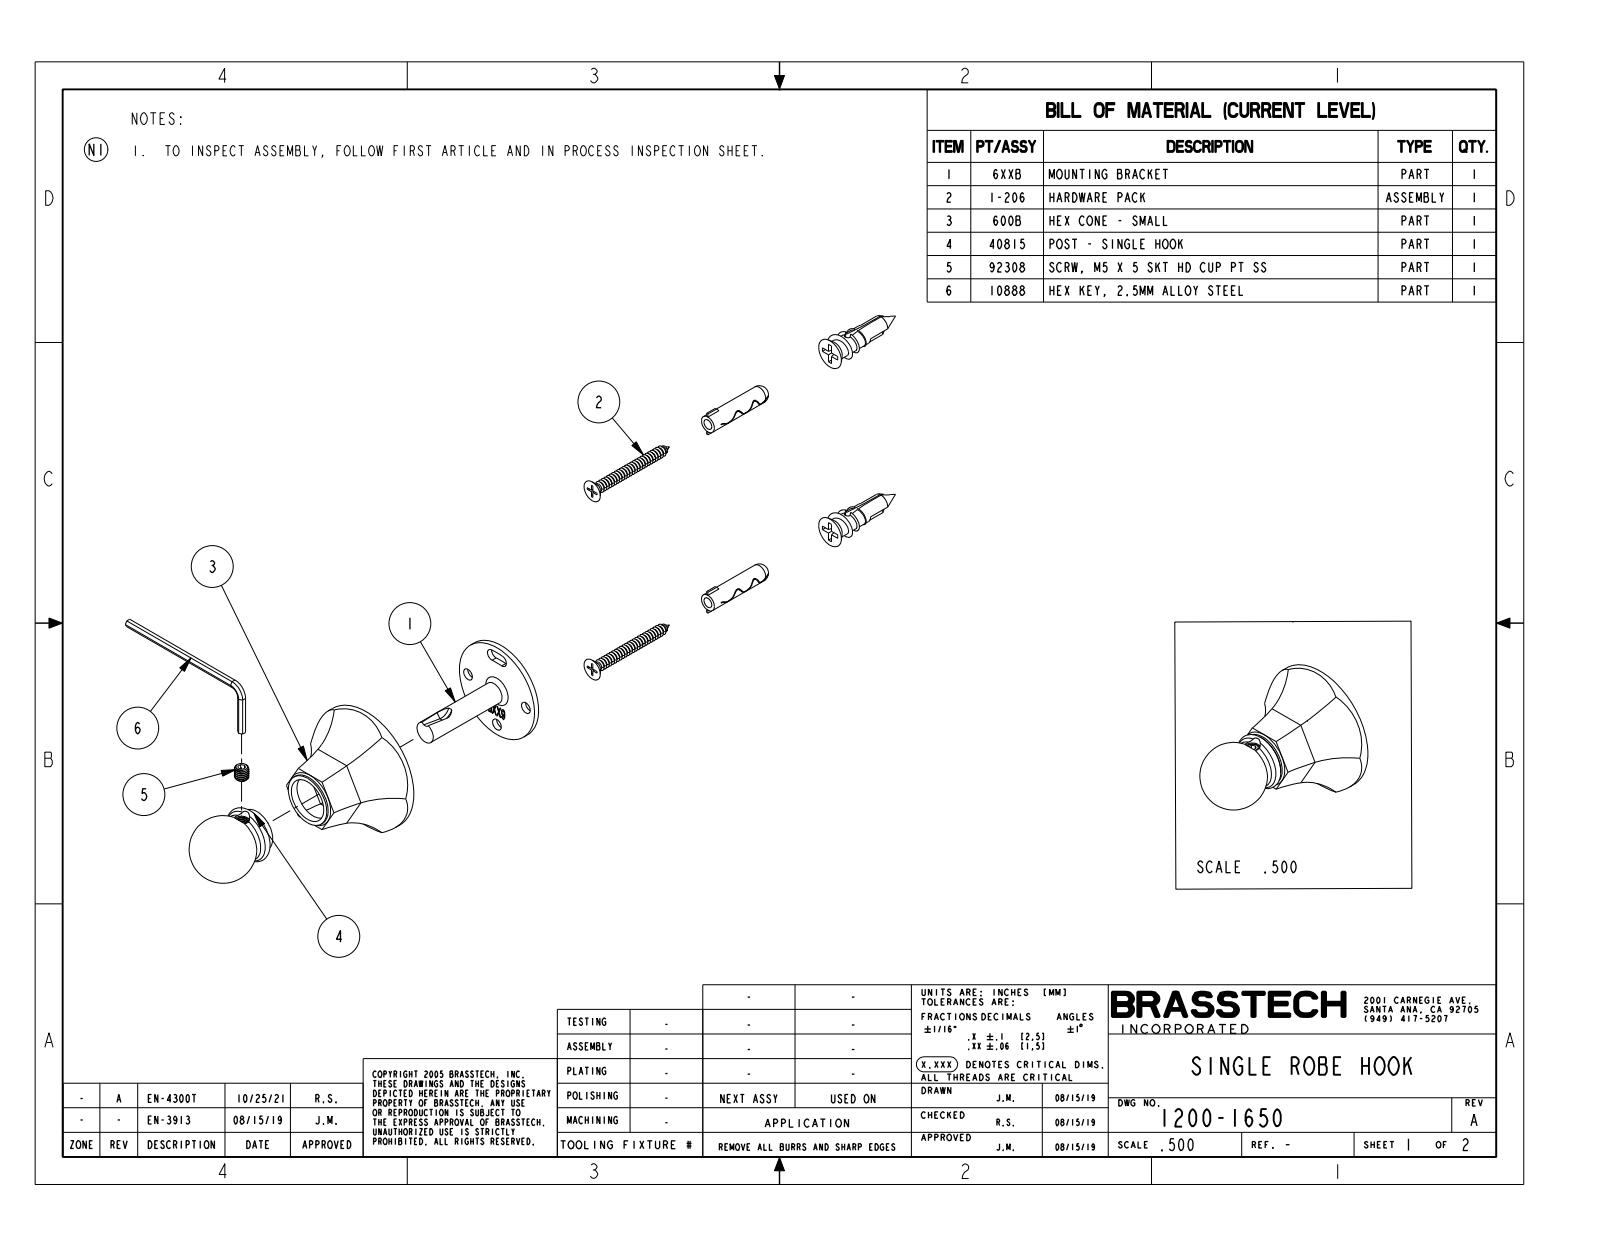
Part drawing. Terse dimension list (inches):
name: 1200-1650
written by: CREO PARAMETRIC BY PTC INC, 2018400 (CONFIG_CONTROL_DESIGN)
unit: in
bodies: 1 solid, 29 faces (3 planar, 18 cylindrical, 8 other)
size: 2.15 × 1.85 × 1.85
volume: 1.858 in³; area: 10.93 in²
bosses: 1× ⌀1.85, 1× ⌀0.748, 1× ⌀0.68
rounds: 6× R0.977, 6× R3.462
face distances: 1.091, 1.142, 0.051
